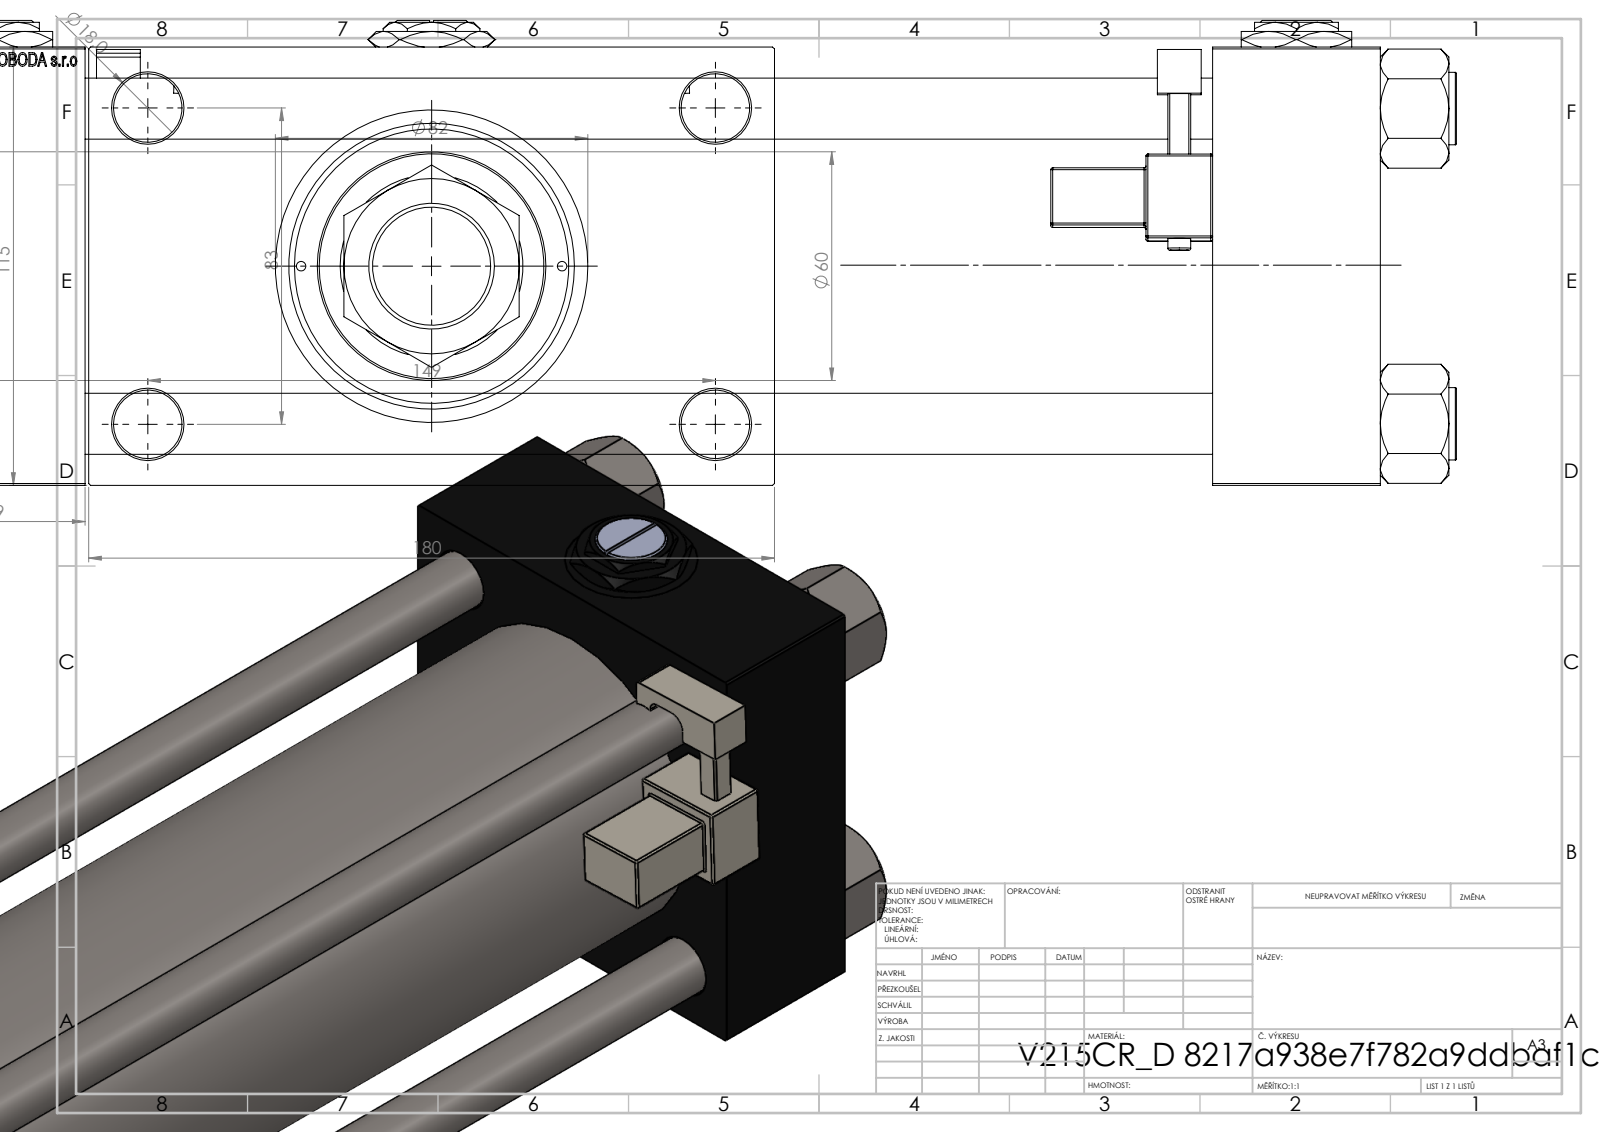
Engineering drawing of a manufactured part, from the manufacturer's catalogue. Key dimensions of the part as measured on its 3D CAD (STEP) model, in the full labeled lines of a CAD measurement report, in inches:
Part name (STEP PRODUCT): V215_VC_A; MTA; V215CR_D_Body; Zatka_pro_OIL_PORT (+4 more)
STEP written by: SolidWorks 2019 (CONFIG_CONTROL_DESIGN)
Units: inches
Bodies: 16 solids, 1463 faces (668 planar, 167 cylindrical, 628 other)
Overall size (bounding box): 20.984 × 7.087 × 4.803
Volume: 174 in³ · Surface area: 825.9 in²
Round holes (diameter × count): ⌀0.63 ×4, ⌀0.709 ×4, ⌀1.041 ×4, ⌀1.378 ×4, ⌀0.276 ×3, ⌀0.098 ×2, ⌀1.24 ×1, ⌀1.772 ×1, ⌀1.89 ×1, ⌀2.402 ×1, ⌀2.835 ×1, ⌀3.15 ×1
Round bosses / shafts (diameter × count): ⌀0.748 ×4, ⌀0.236 ×2, ⌀3.386 ×1, ⌀3.228 ×1, ⌀2.362 ×1, ⌀1.299 ×1, ⌀1.22 ×1
Partial cylindrical surfaces — rounded edges, fillets, slot ends (radius × count): R0.02 ×48, R0.039 ×2, R0.098 ×2, R0.157 ×2, R0.866 ×1
Main face-to-face distances: 4.528, 11.654, 13.583, 1.929, 1.732, 13.386, 15.315, 1.28, 5.807, 1.811
Hole centre spacings: 1.305, 1.652, 2.276, 2.302, 3.256, 3.357, 3.393, 3.513
